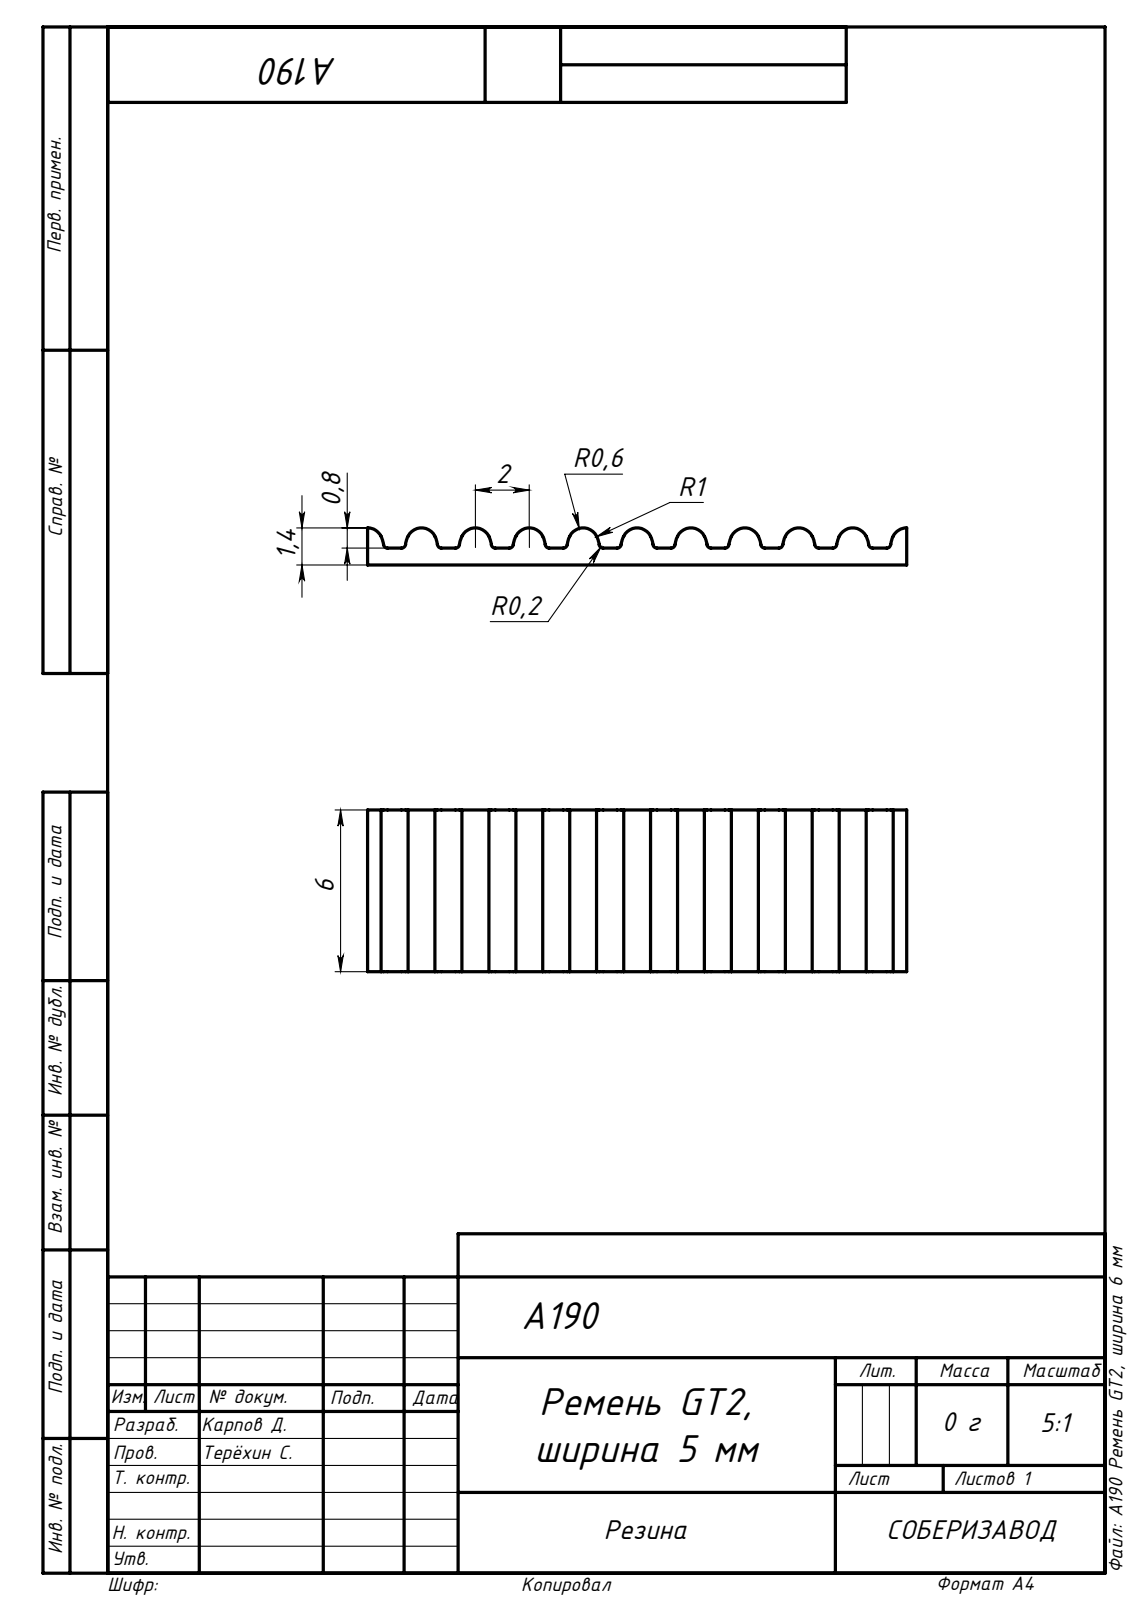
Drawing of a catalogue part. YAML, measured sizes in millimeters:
part_name: "01.01.01.21"
step_written_by: "SolidWorks 2018 (CONFIG_CONTROL_DESIGN)"
units: millimeters
bodies: {solids: 1, faces: 66, planar: 15, cylindrical: 51, other: 0}
overall_size: [20, 6, 1.38]
volume: 119
surface_area: 347
partial_cylinders:
  - {radius: 0.15, count: 20}
  - {radius: 1, count: 20}
  - {radius: 0.56, count: 11}
face_to_face_distances: [0.63, 6, 20]
